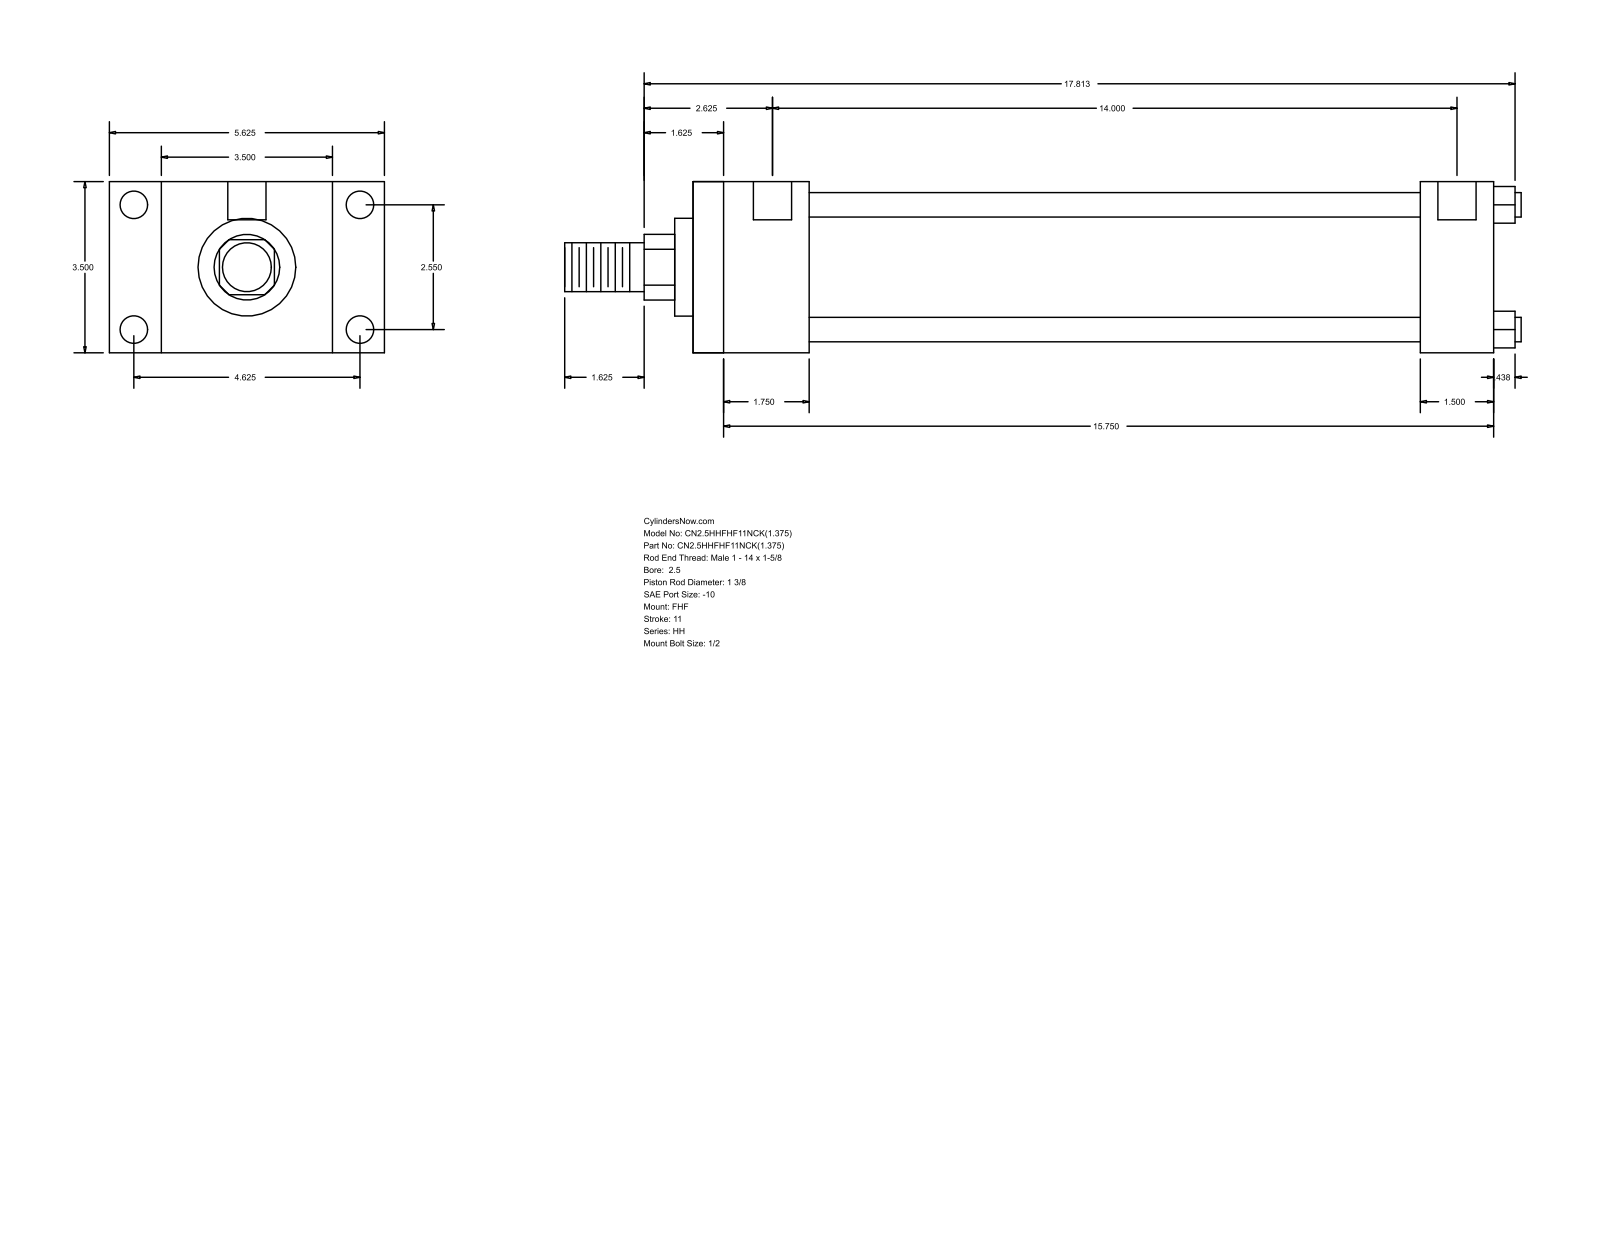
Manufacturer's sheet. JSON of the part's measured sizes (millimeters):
{"part_name": "HH_FHF__0250_1.375", "step_written_by": "GSSL Pune (CONFIG_CONTROL_DESIGN)", "units": "millimeters", "bodies": {"solids": 0, "faces": 88, "planar": 60, "cylindrical": 28, "other": 0}, "overall_size": [496.89, 142.88, 88.9], "round_holes": [[5.56, 4], [14.3, 4], [19.84, 2]], "round_bosses_or_shafts": [[12.7, 4], [73.03, 1], [50.8, 1], [34.92, 1], [25.4, 1]], "partial_cylinders_radius": [[17.06, 1]], "face_to_face_distances": [88.9, 60.32, 26.99, 115.89, 415.92, 355.6, 142.88, 377.83, 317.51, 38.09], "hole_center_spacings": [64.76, 117.48, 134.15, 358.77, 1.58, 1.59, 355.6, 357.18]}
